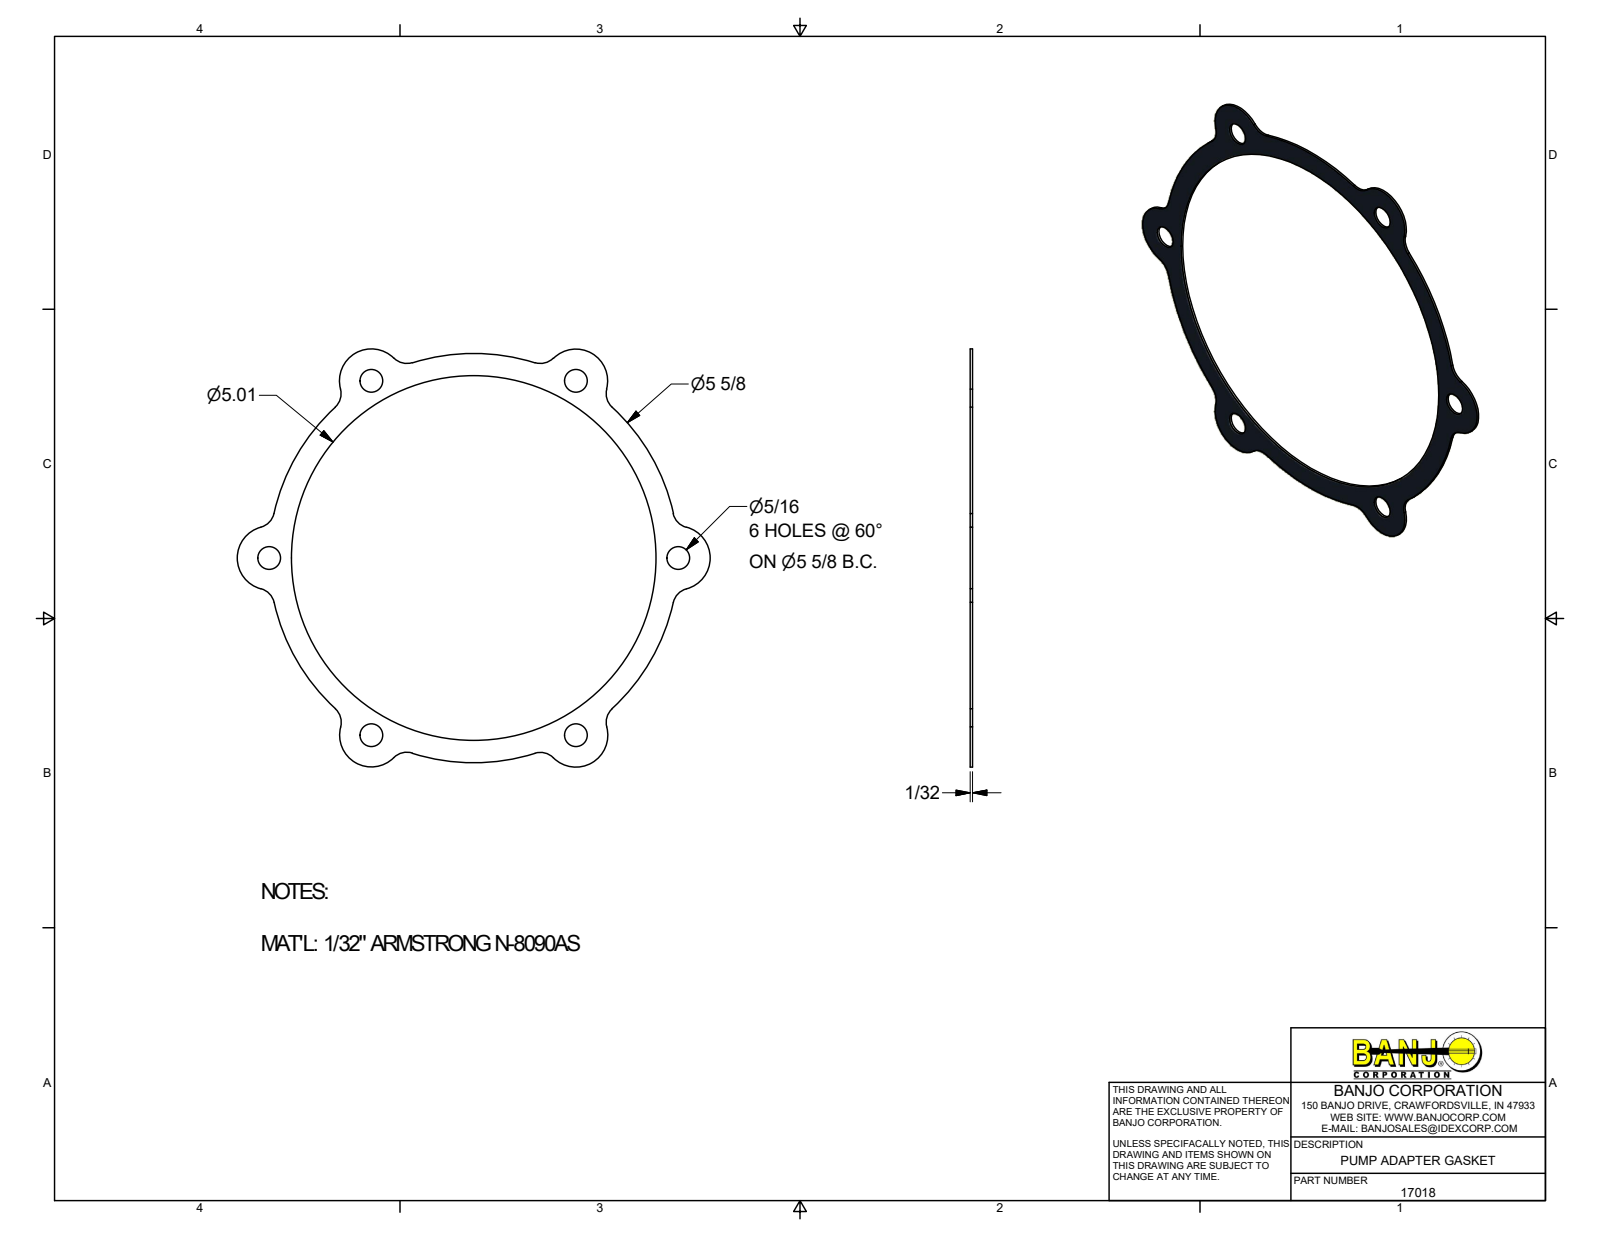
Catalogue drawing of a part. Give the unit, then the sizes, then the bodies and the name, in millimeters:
Units: millimetres
Overall size (bounding box): 165.1 × 145.96 × 0.79
Round holes (diameter × count): ⌀7.94 ×6, ⌀127.25 ×1
Partial cylindrical surfaces — rounded edges, fillets, slot ends (radius × count): R6.35 ×12, R11.11 ×6, R71.44 ×1
Main face-to-face distances: 0.79
Hole centre spacings: 71.44, 123.74, 142.88
Volume: 3 382 mm³ · Surface area: 9 371 mm²
Bodies: 1 solid, 33 faces (2 planar, 31 cylindrical, 0 other)
Part name (STEP PRODUCT): 17018
STEP written by: Autodesk Inventor 2017 (AUTOMOTIVE_DESIGN)
